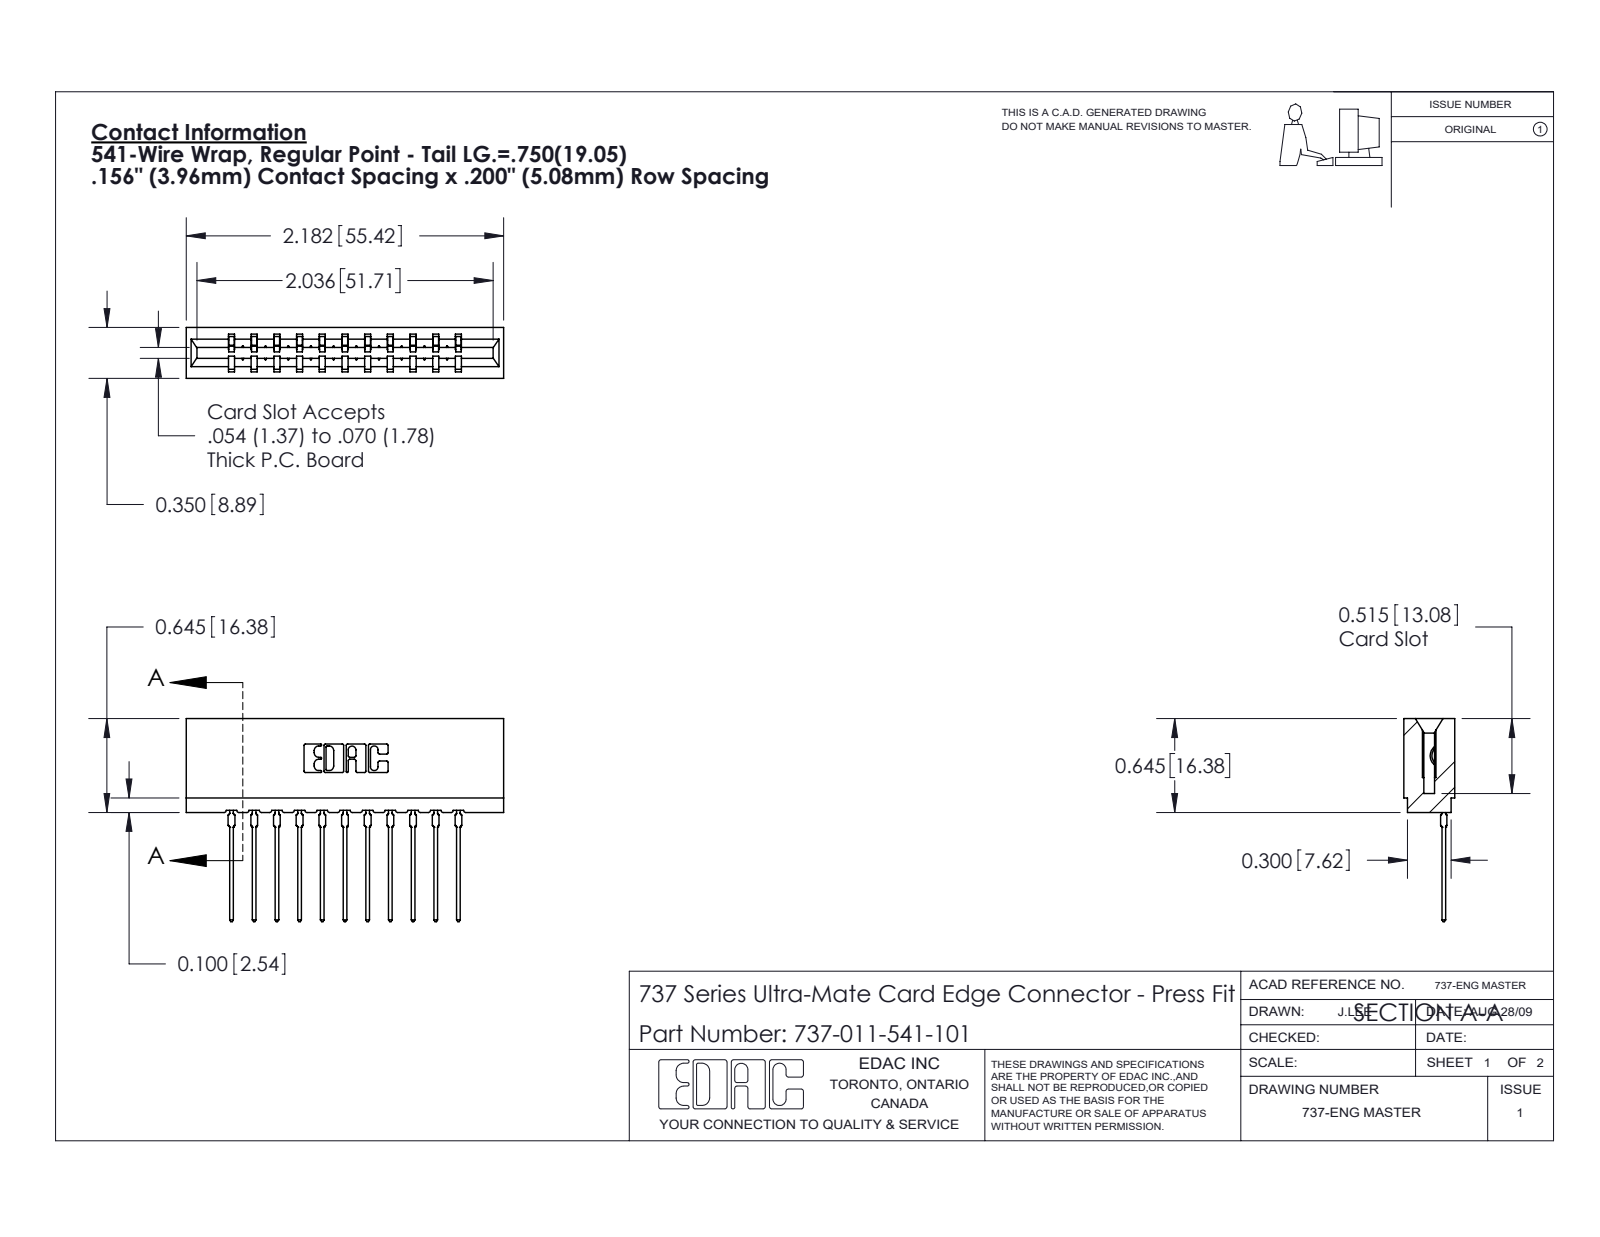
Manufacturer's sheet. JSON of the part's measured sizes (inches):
{"part_name": "737 Part_Insulator Option - 01; 737-011-541-101; 745-292-001_541", "step_written_by": "SolidWorks 2020 (CONFIG_CONTROL_DESIGN)", "units": "inches", "bodies": {"solids": 12, "faces": 1337, "planar": 802, "cylindrical": 249, "other": 286}, "overall_size": [2.182, 1.396, 0.35], "volume_in3": 0.343, "surface_area_in2": 11.18, "partial_cylinders_radius": [[0.01, 22], [0.015, 22], [0.021, 22], [0.007, 6], [0.031, 6], [0.005, 4], [0.011, 4], [0.026, 3]], "face_to_face_distances": [0.138, 0.212, 0.156, 0.35, 0.624, 0.312, 0.468, 0.78, 0.27, 0.354]}
